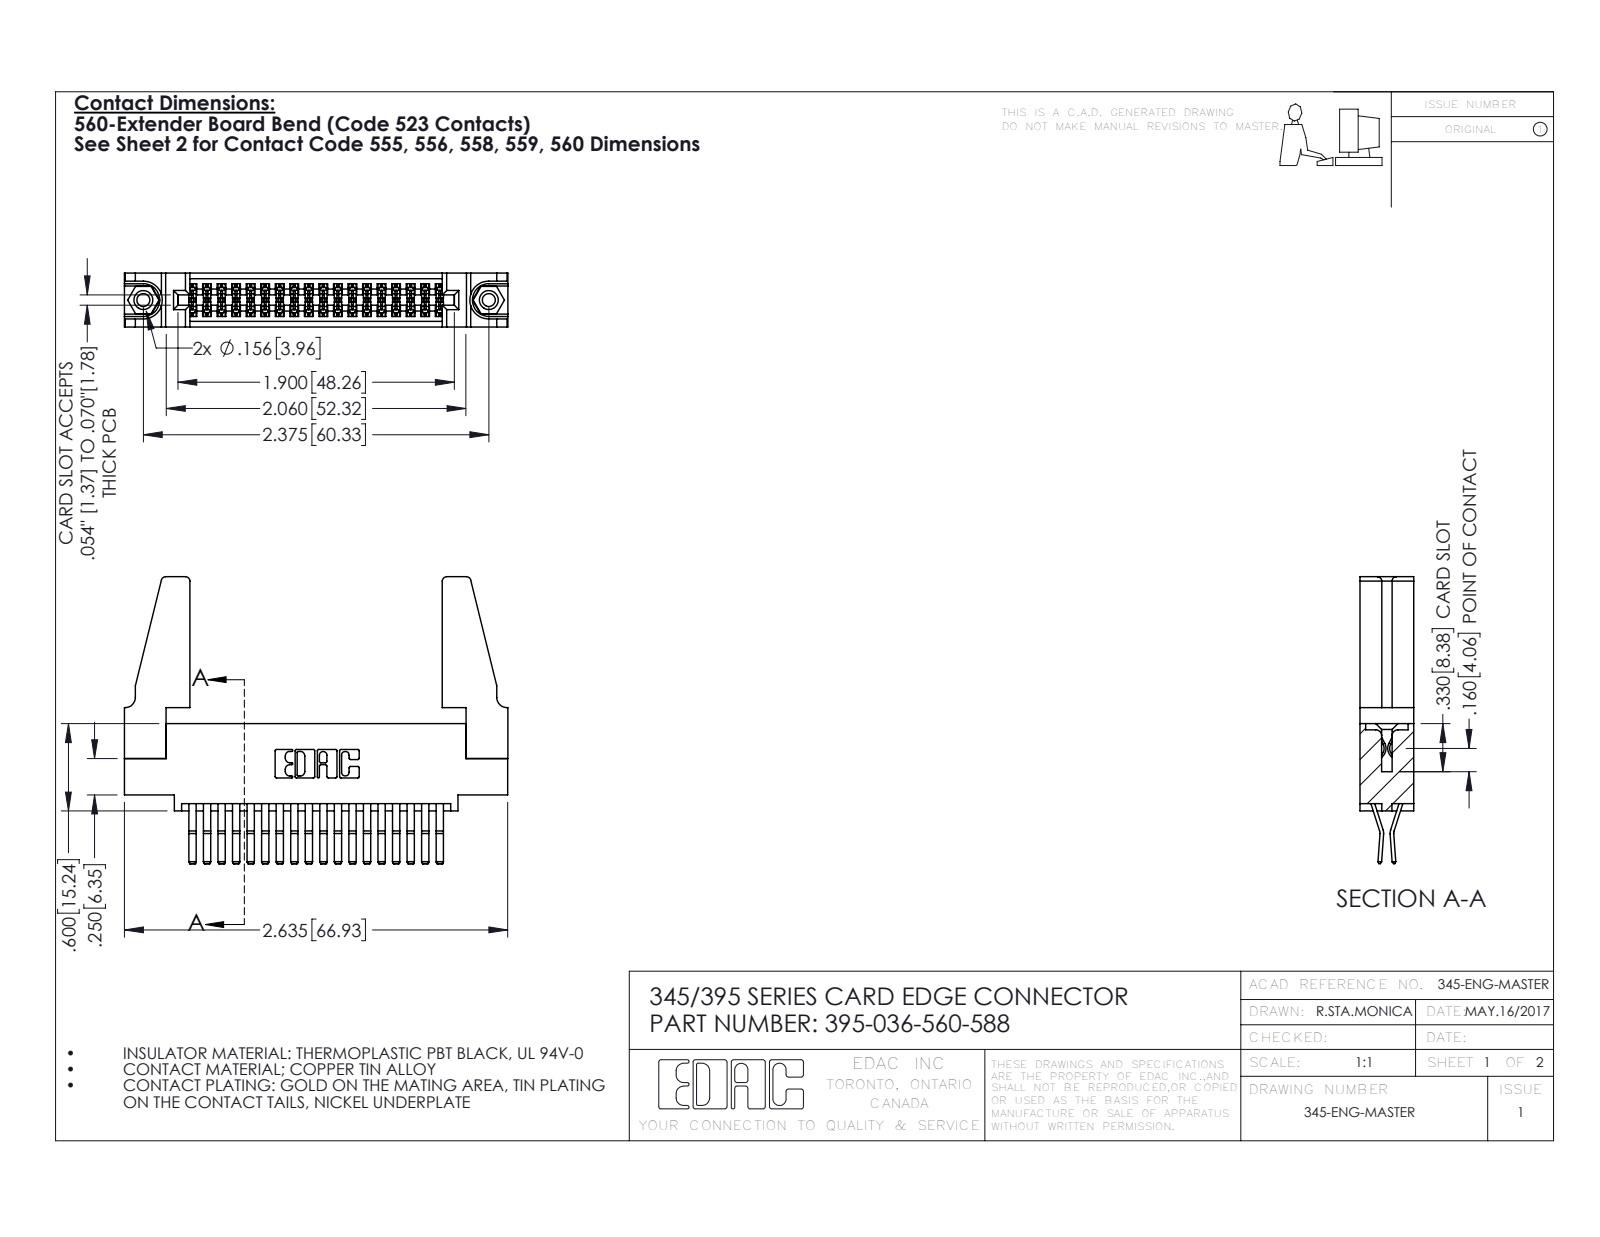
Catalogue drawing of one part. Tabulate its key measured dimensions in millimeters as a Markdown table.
| quantity | value |
| --- | --- |
| part name | 345-250-001_345-250-001-102; 345-220-078_345-220-088; 395-036-560-588; 345 Part_0.110 Offset - 0.156 Dia-TH (+1 more) |
| STEP written by | SolidWorks 2016 (CONFIG_CONTROL_DESIGN) |
| units | millimeters |
| bodies | 41 solids, 2126 faces (1344 planar, 766 cylindrical, 16 other) |
| overall size | 67 × 50.1 × 9.4 |
| volume | 9 700 mm³ |
| surface area | 12 880 mm² |
| round holes (diameter × count) | 2.3 × 2, 3.2 × 2, 4 × 2, 1.6 × 1 |
| round bosses / shafts (diameter × count) | 3.9 × 2 |
| partial cylindrical surfaces (radius × count) | 0.2 × 54, 0.3 × 22, 0.8 × 8, 0.2 × 6, 0.8 × 6, 0.7 × 3, 0.3 × 2, 0.4 × 2 |
| main face-to-face distances | 9.4, 1.8, 7.6, 0.6, 5.1, 2.5, 6.9, 5.7, 4.4, 3.8 |
| hole center spacings | 6.9, 54.4, 60.3 |
